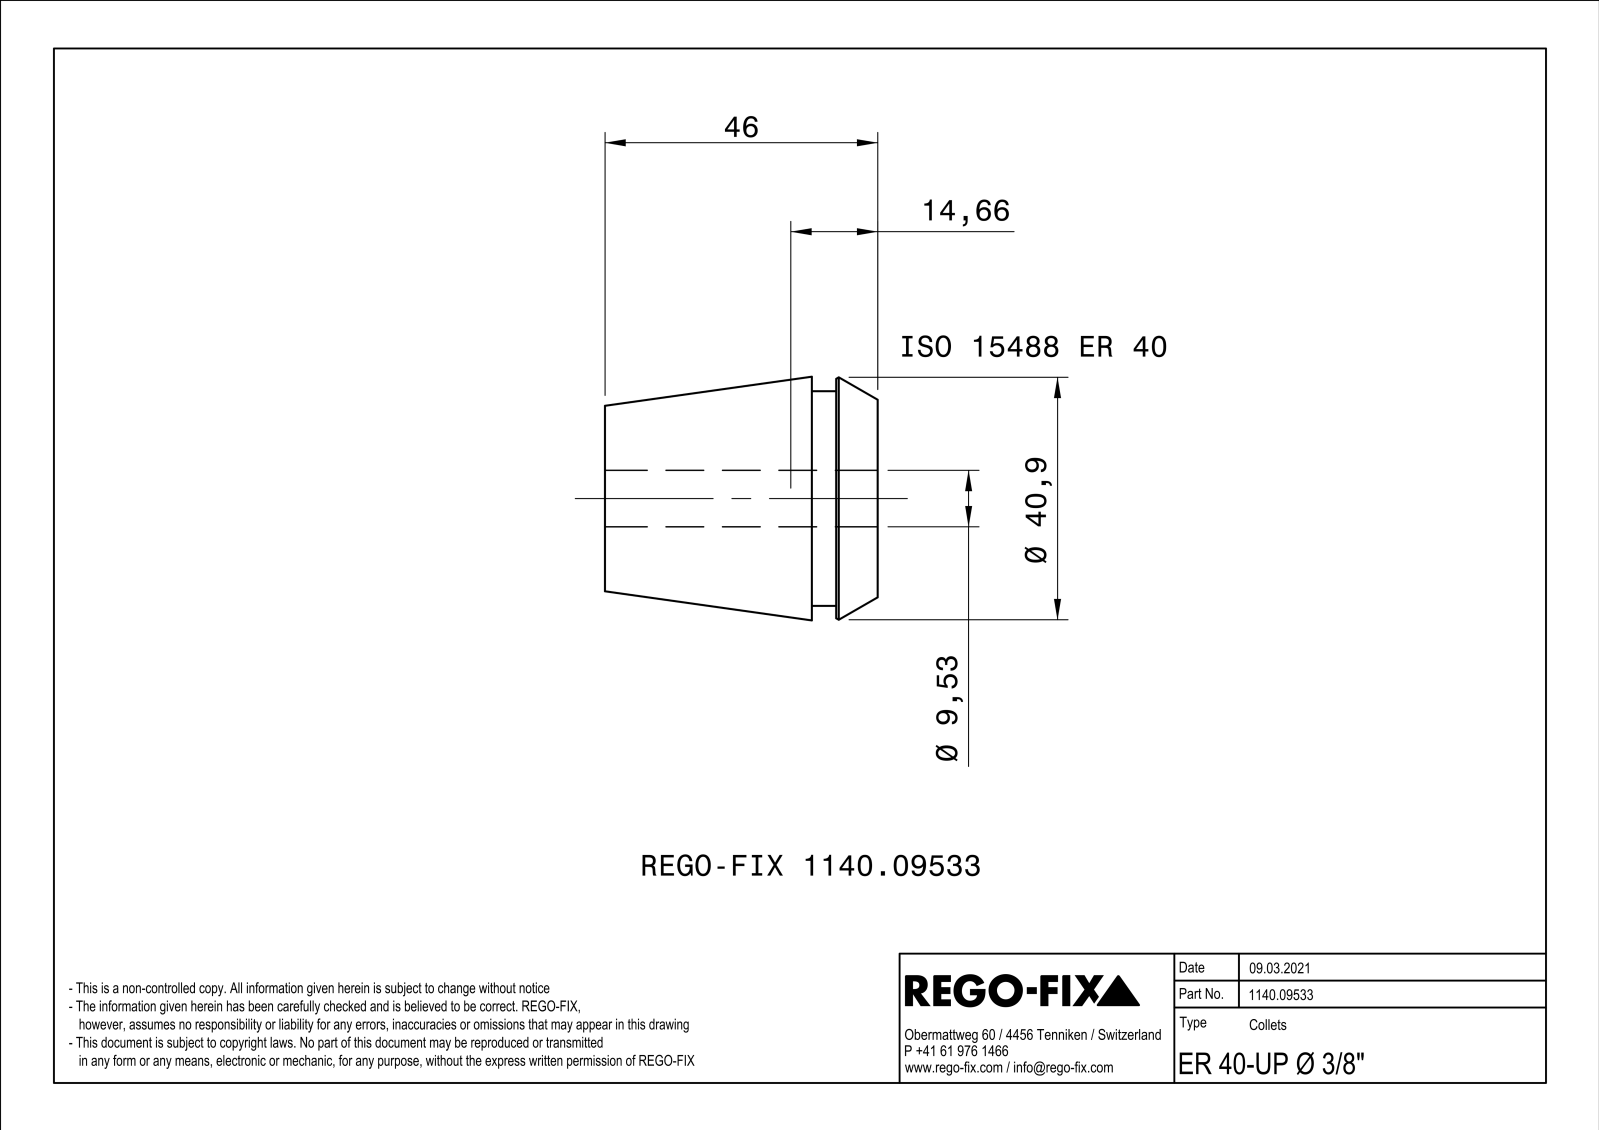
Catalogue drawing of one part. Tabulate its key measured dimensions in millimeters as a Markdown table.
| quantity | value |
| --- | --- |
| part name | NOCUT |
| STEP written by | SIEMENS PLM Software Solid Edge ST10 (AUTOMOTIVE_DESIGN) |
| units | millimeters |
| bodies | 1 solid, 177 faces (88 planar, 9 cylindrical, 80 other) |
| overall size | 46 × 40.99 × 40.99 |
| volume | 35 846 mm³ |
| surface area | 24 871 mm² |
| round holes (diameter × count) | 9.53 × 1 |
| round bosses / shafts (diameter × count) | 36.2 × 1 |
| main face-to-face distances | 1, 46, 11.1, 34.9, 7, 4.1, 39, 7.5, 0.5, 3.6 |
